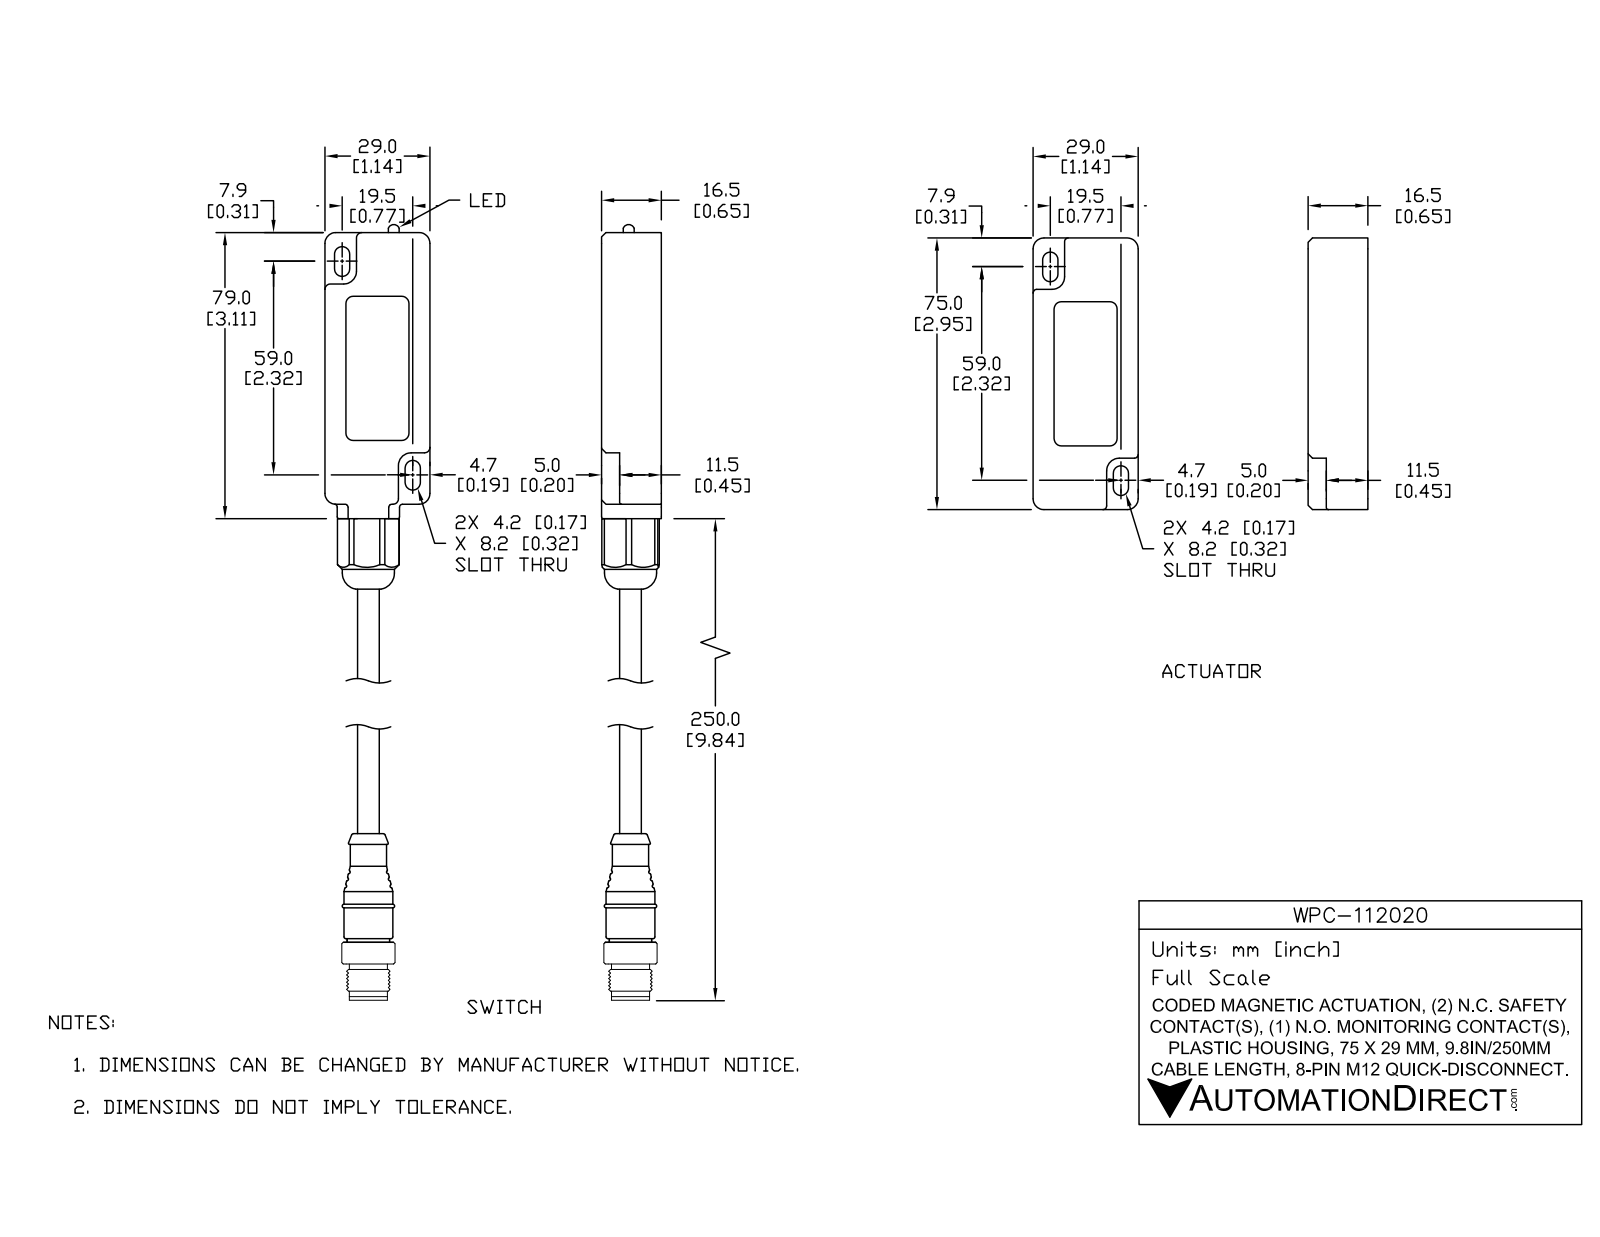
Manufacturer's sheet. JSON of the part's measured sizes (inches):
{"part_name": "WPC-112020_1; WPC-112020; WPC-112020_2", "step_written_by": "SolidWorks 2017 (AUTOMOTIVE_DESIGN)", "units": "inches", "bodies": {"solids": 12, "faces": 1311, "planar": 577, "cylindrical": 358, "other": 376}, "overall_size": [13.039, 2.323, 0.65], "volume_in3": 2.632, "surface_area_in2": 65.51, "round_holes": [[0.195, 4], [0.118, 1], [0.276, 1], [0.327, 1], [0.465, 1], [0.472, 1]], "round_bosses_or_shafts": [[0.031, 10], [0.193, 4], [0.079, 4], [0.091, 2], [0.567, 1], [0.531, 1], [0.469, 1], [0.461, 1]], "partial_cylinders_radius": [[0.02, 85], [0.039, 20], [0.008, 10], [0.047, 8], [0.079, 8], [0.083, 8], [0.118, 8], [0.024, 4]], "face_to_face_distances": [0.071, 0.575, 1.181, 1.071, 0.646, 0.067, 0.571, 0.075, 0.504, 0.579], "hole_center_spacings": [2.047, 0.276, 0.9, 1.459, 2.344, 2.347]}
